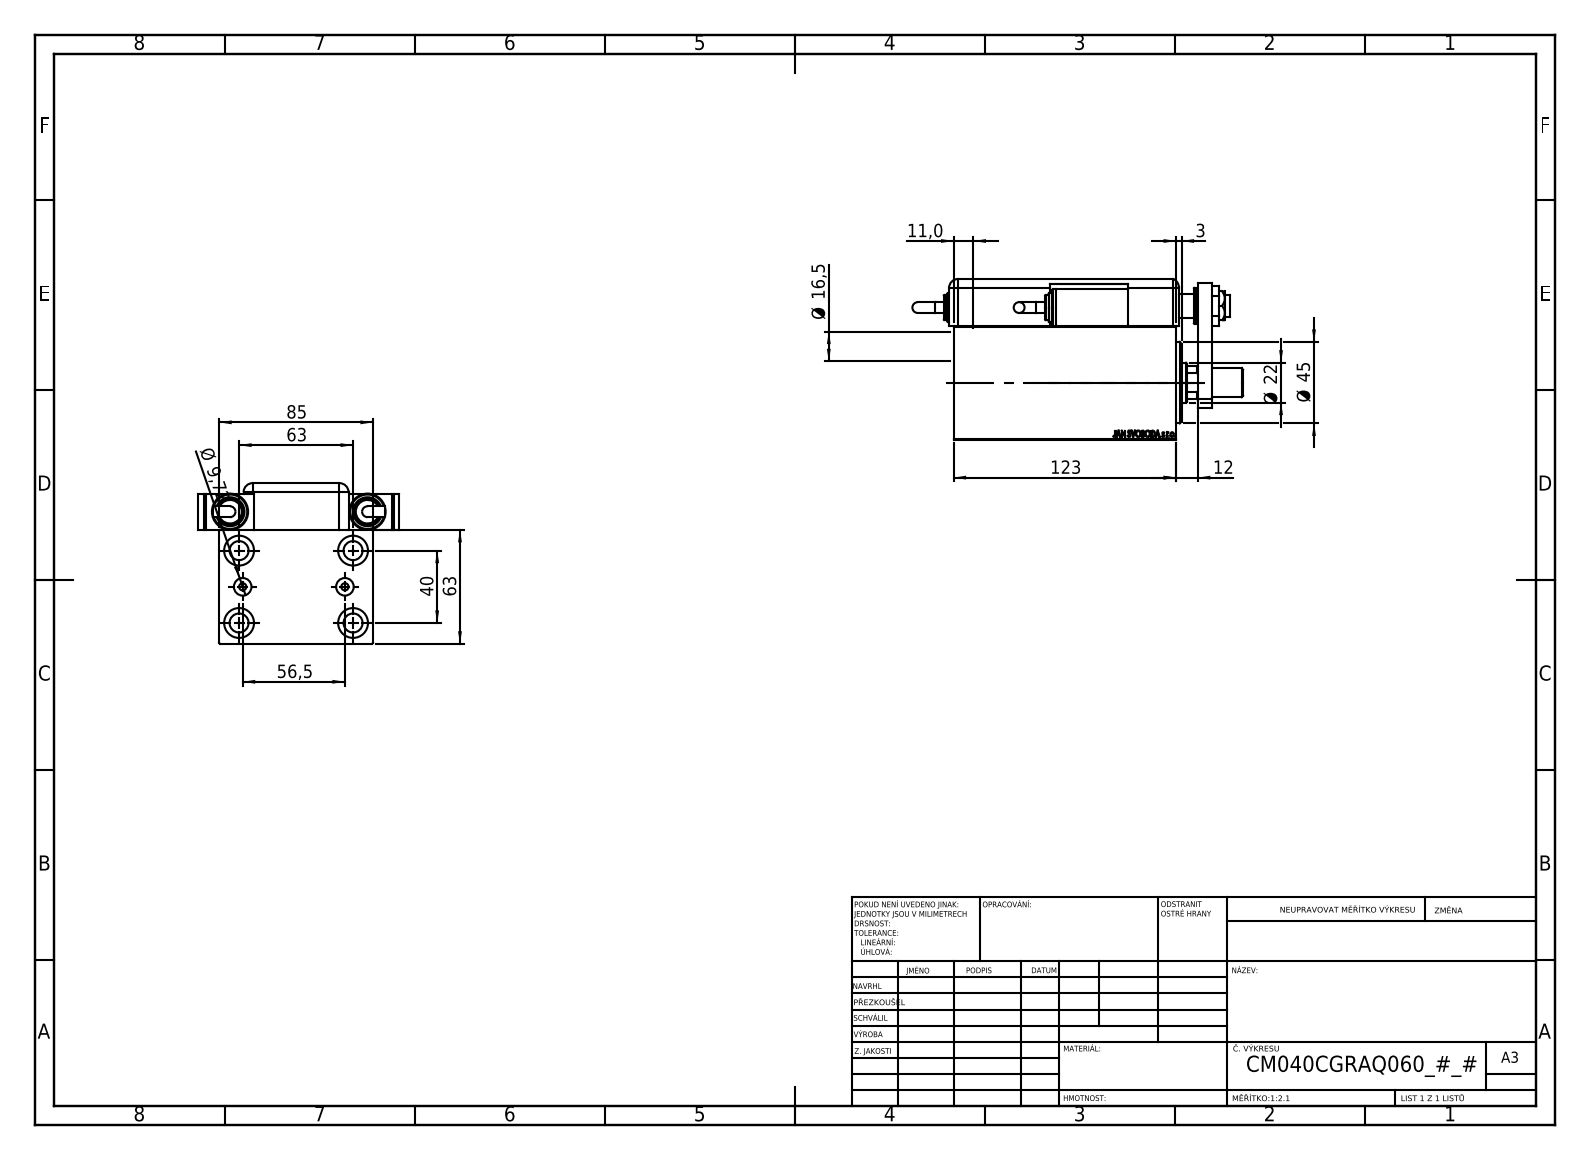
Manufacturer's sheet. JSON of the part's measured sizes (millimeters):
{"part_name": "SWITCH_Q_FRONT_BACK; V450CM_MALE_METRIC; SWITCH Q; SWITCH DIM A_G (+7 more)", "step_written_by": "SolidWorks 2019 (CONFIG_CONTROL_DESIGN)", "units": "millimeters", "bodies": {"solids": 14, "faces": 1256, "planar": 618, "cylindrical": 115, "other": 523}, "overall_size": [182.76, 111, 88.8], "volume_mm3": 707768, "surface_area_mm2": 162036, "round_holes": [[4, 4], [10.5, 4], [16.5, 4], [8, 2], [9.72, 2], [14, 2], [12, 1], [12.5, 1], [13, 1], [22, 1], [25.5, 1], [40, 1]], "round_bosses_or_shafts": [[20, 3], [16, 3], [14, 3], [6, 2]], "partial_cylinders_radius": [[5, 9], [10, 1], [10.5, 1]], "face_to_face_distances": [3, 63, 85, 13.5, 25.8, 88.8, 12, 16.5, 123, 20], "hole_center_spacings": [37.31, 20.1, 20.5, 36.79, 37.86, 38.71, 40, 61.82]}
